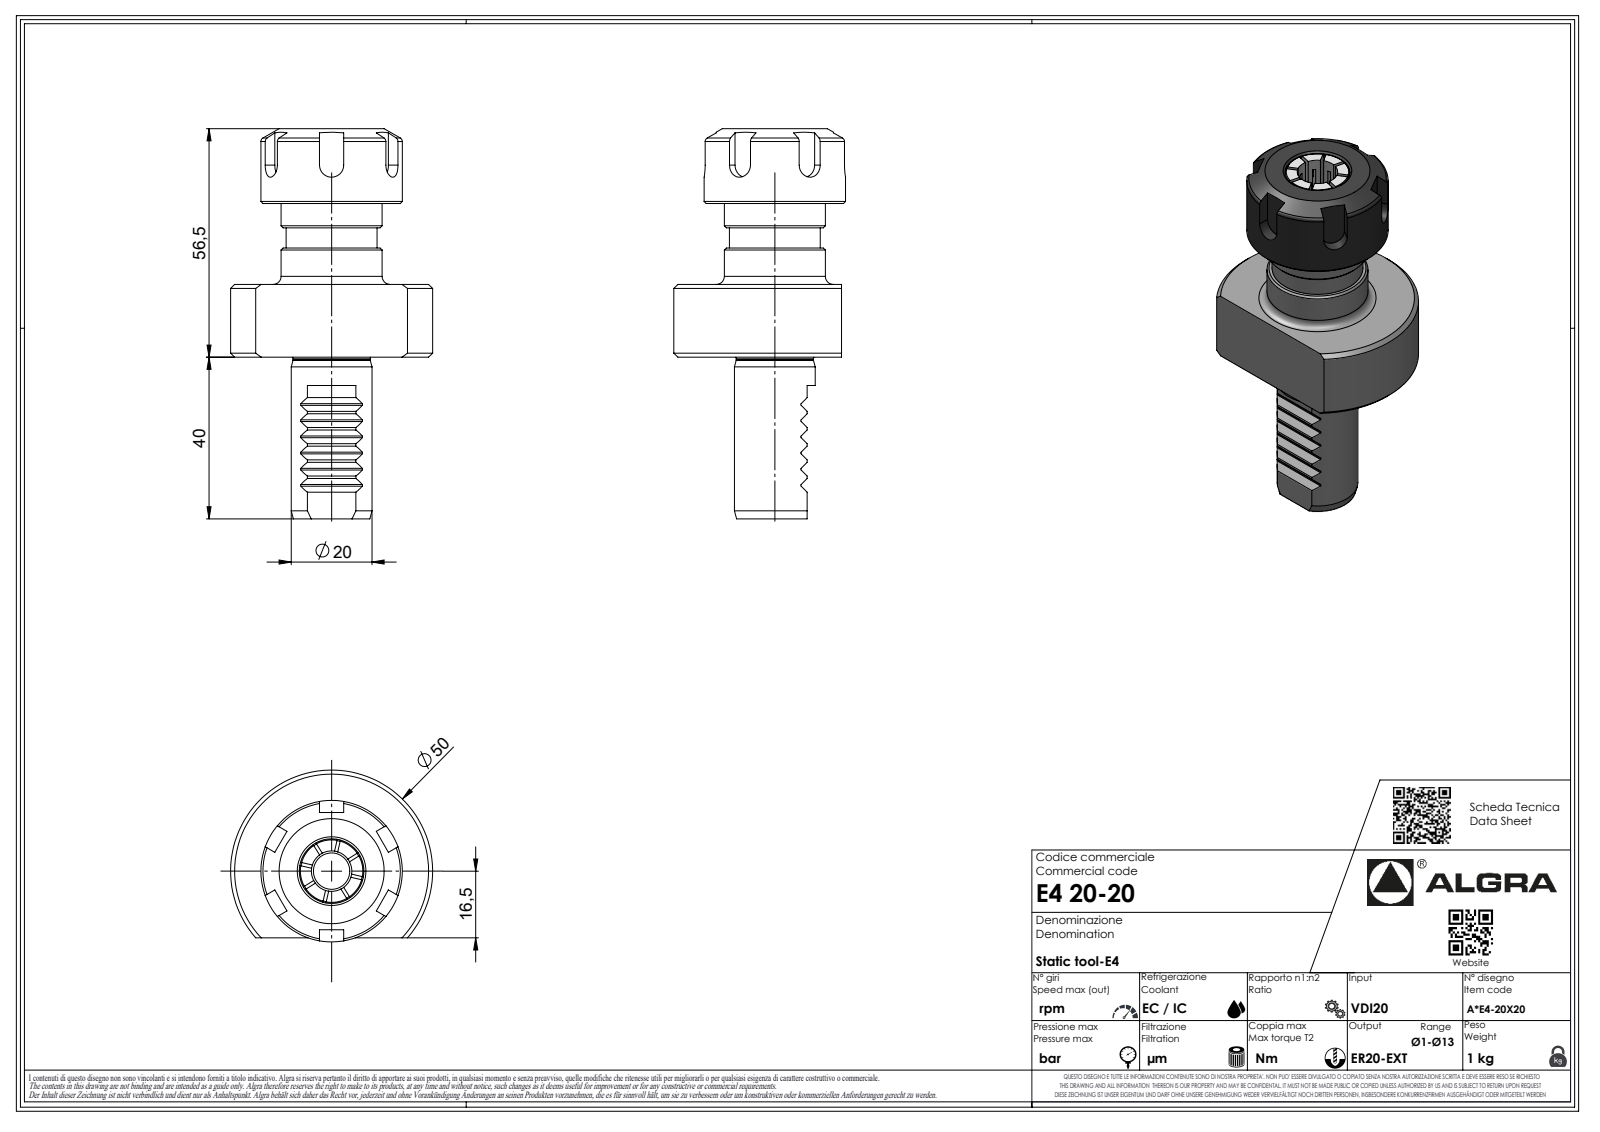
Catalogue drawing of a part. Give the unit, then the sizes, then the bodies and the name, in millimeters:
Units: millimetres
Overall size (bounding box): 96.52 × 50 × 42.5
Round holes (diameter × count): ⌀2.1 ×1
Round bosses / shafts (diameter × count): ⌀35 ×1, ⌀25 ×1, ⌀22.5 ×1, ⌀20 ×1, ⌀19.1 ×1, ⌀6.37 ×1, ⌀1.7 ×1
Partial cylindrical surfaces — rounded edges, fillets, slot ends (radius × count): R0.33 ×7, R0.52 ×7, R3.7 ×7, R0.3 ×6, R3 ×3, R0.21 ×1, R25 ×1
Main face-to-face distances: 18, 56.52, 38.52, 38.02, 20.02, 18.5, 40, 58, 78.02, 96.52
Volume: 68 508 mm³ · Surface area: 13 431 mm²
Bodies: 1 solid, 283 faces (185 planar, 45 cylindrical, 53 other)
Part name (STEP PRODUCT): E420-20
STEP written by: SolidWorks 2023 (AUTOMOTIVE_DESIGN)
